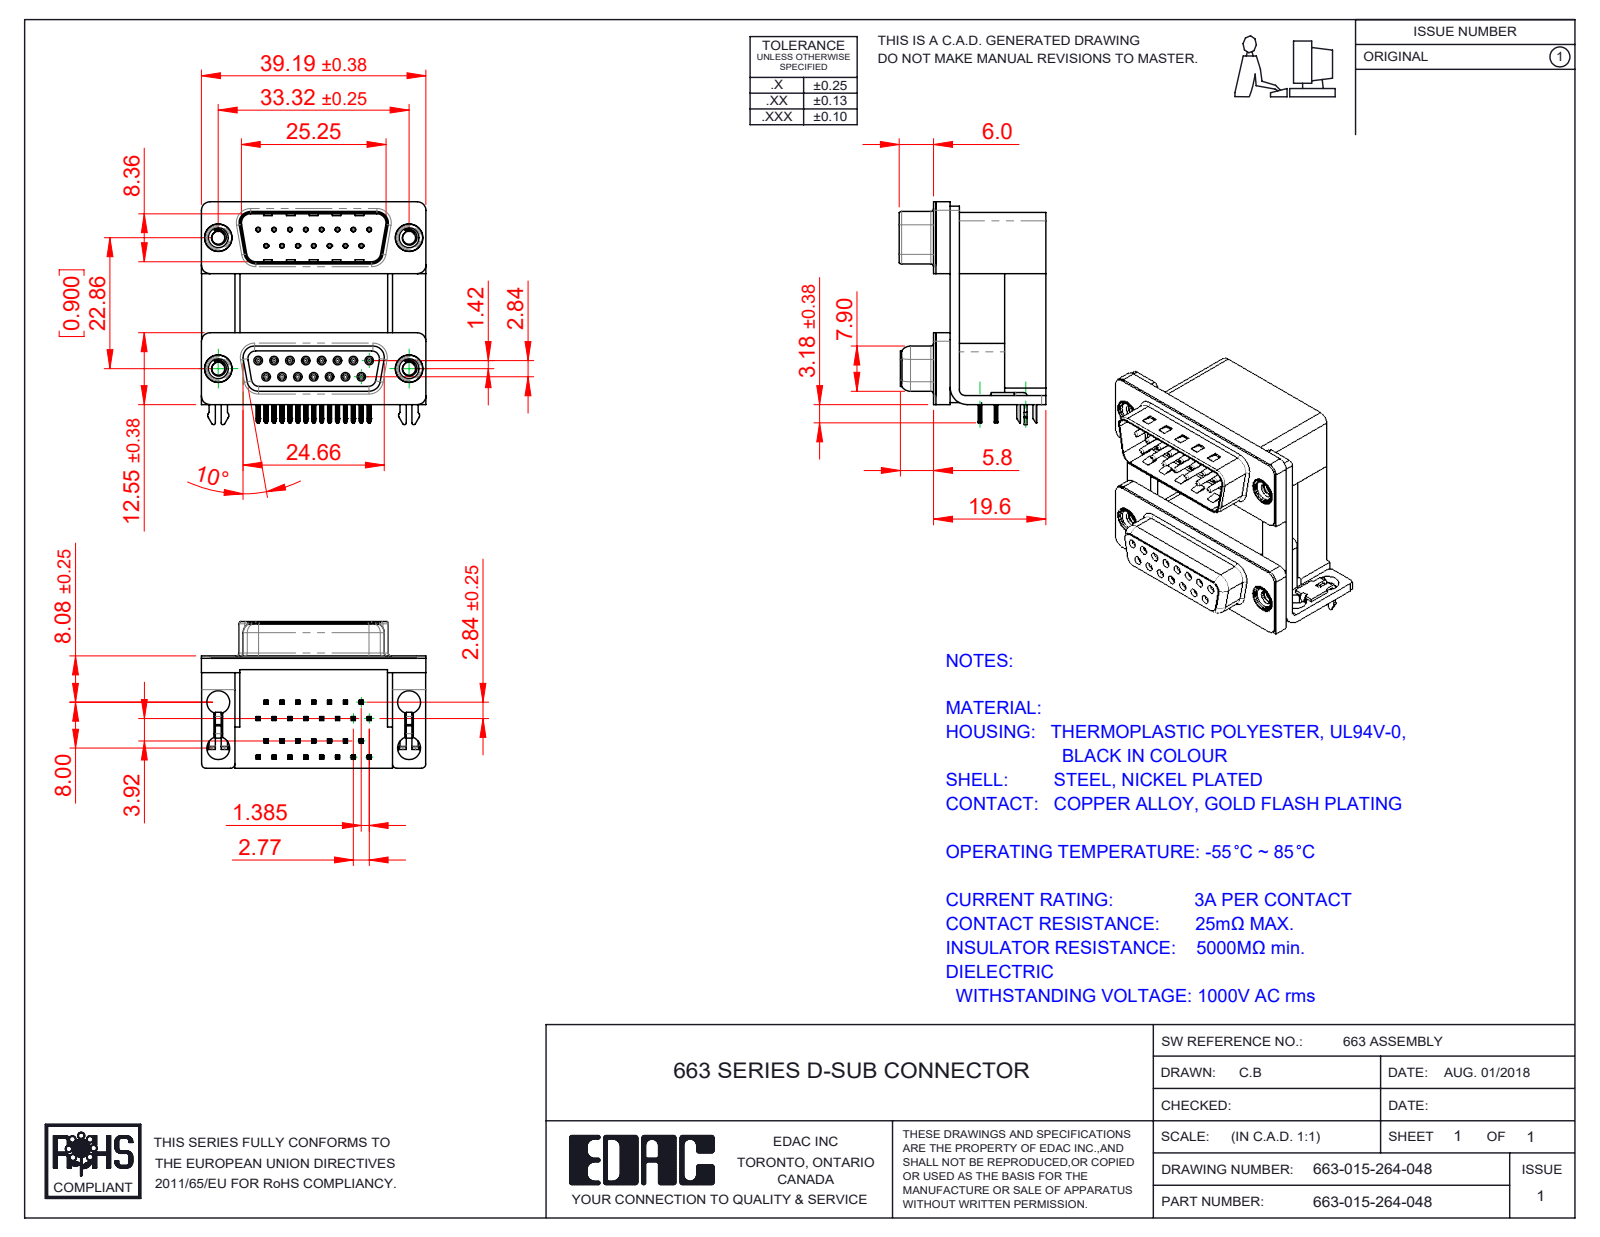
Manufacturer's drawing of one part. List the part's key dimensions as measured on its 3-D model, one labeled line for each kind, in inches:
Part name (STEP PRODUCT): 663 Contact Top Lower; 663 Housing Upper_15 Contacts H; 663 Threaded Rivet_4-40; 663 Contact Bottom Upper_H (+8 more)
STEP written by: SolidWorks 2020 (CONFIG_CONTROL_DESIGN)
Units: inches
Bodies: 43 solids, 4020 faces (2093 planar, 1044 cylindrical, 883 other)
Overall size (bounding box): 1.543 × 1.532 × 1.008
Volume: 0.976 in³ · Surface area: 27.3 in²
Round holes (diameter × count): ⌀0.031 ×30, ⌀0.014 ×15, ⌀0.035 ×15, ⌀0.157 ×8, ⌀0.089 ×4, ⌀0.138 ×4, ⌀0.189 ×4, ⌀0.197 ×4
Round bosses / shafts (diameter × count): ⌀0.047 ×15, ⌀0.03 ×15, ⌀0.193 ×4, ⌀0.187 ×4, ⌀0.154 ×4
Partial cylindrical surfaces — rounded edges, fillets, slot ends (radius × count): R0.004 ×121, R0.01 ×66, R0.006 ×60, R0.005 ×30, R0.014 ×30, R0.02 ×16, R0.059 ×16, R0.013 ×15
Main face-to-face distances: 0.756, 0.016, 0.472, 0.283, 0.657, 0.374, 0.098, 0.421, 0.488, 0.063
Hole centre spacings: 0.124, 0.907, 0.109, 0.926, 0.218, 0.327, 0.9, 0.957
